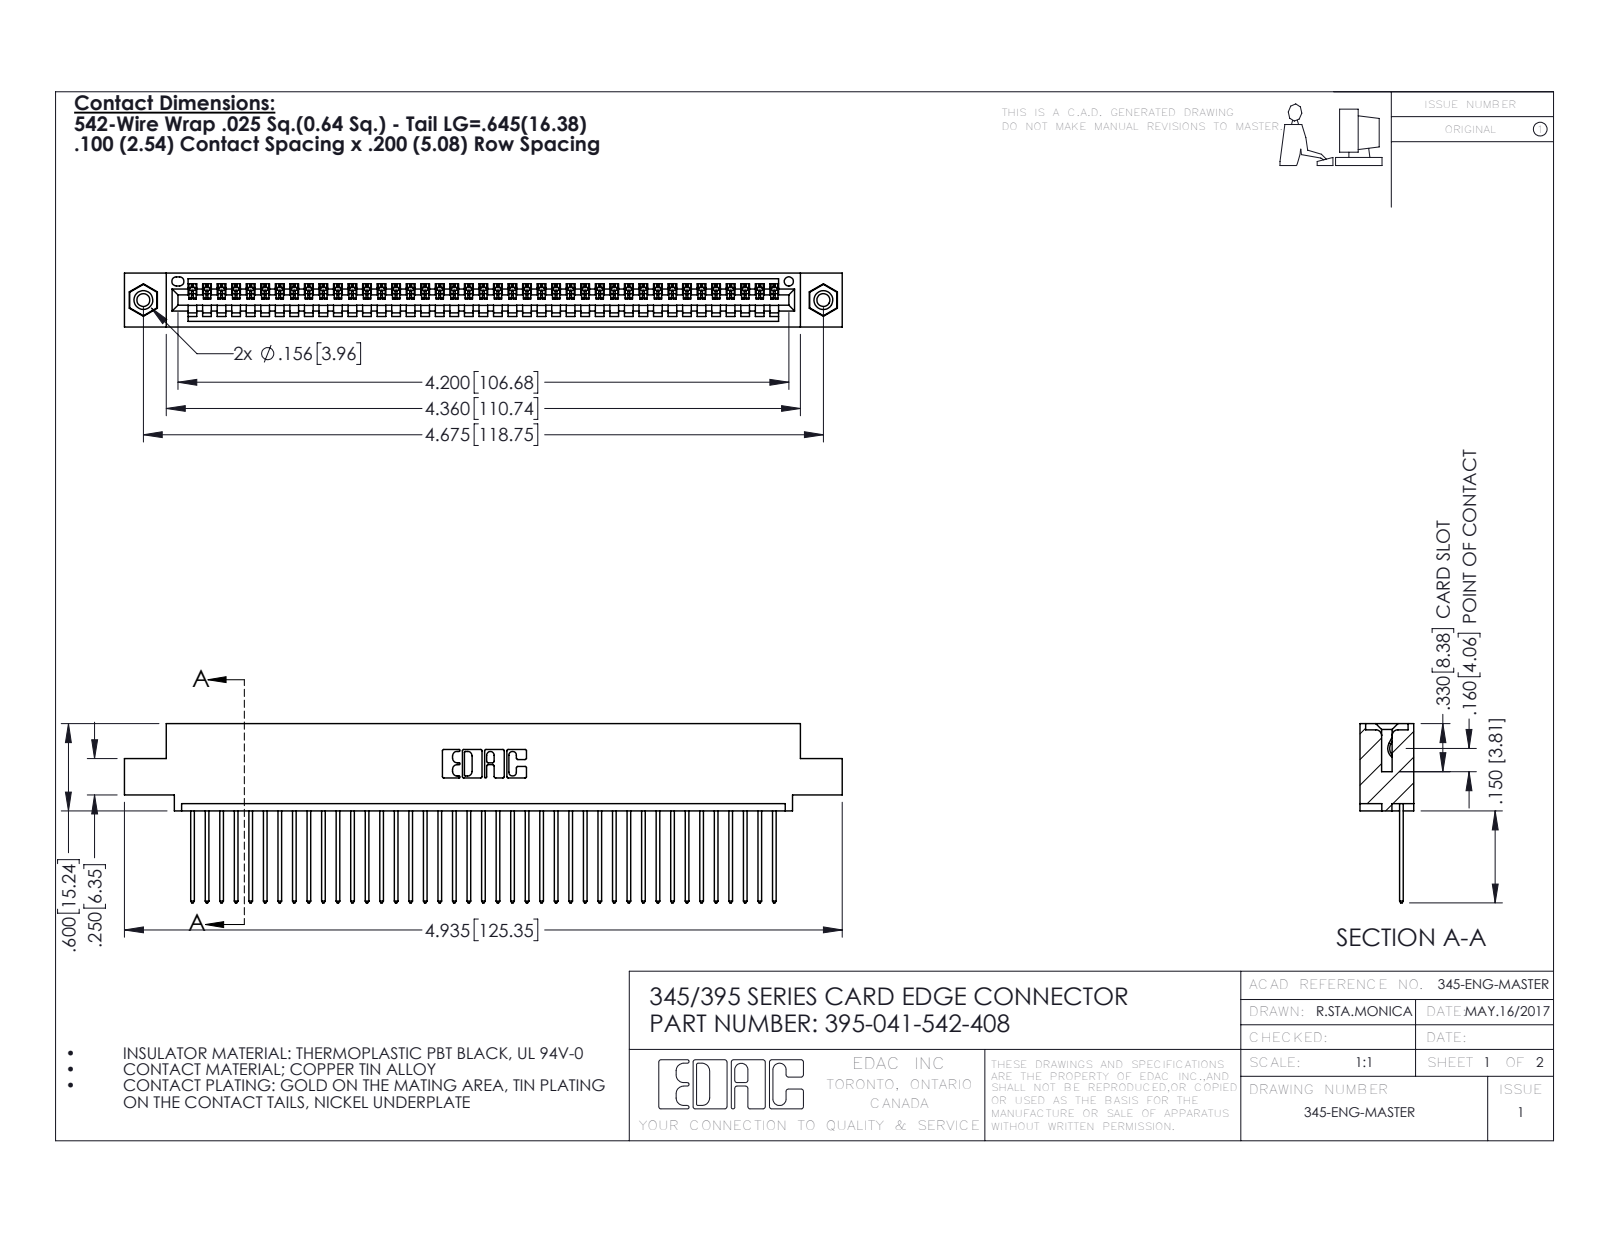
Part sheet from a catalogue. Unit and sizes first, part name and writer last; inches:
Units: inches
Overall size (bounding box): 4.935 × 1.232 × 0.37
Round holes (diameter × count): ⌀0.089 ×2, ⌀0.125 ×2, ⌀0.156 ×2, ⌀0.064 ×1
Round bosses / shafts (diameter × count): ⌀0.155 ×2
Partial cylindrical surfaces — rounded edges, fillets, slot ends (radius × count): R0.006 ×82, R0.01 ×82, R0.01 ×22, R0.007 ×6, R0.031 ×6, R0.026 ×3, R0.031 ×2, R0.04 ×2
Main face-to-face distances: 0.072, 0.298, 0.37, 0.098, 0.272, 0.025, 0.2, 0.225, 0.149, 0.072
Hole centre spacings: 0.27, 4.439, 4.675
Volume: 0.727 in³ · Surface area: 25.56 in²
Bodies: 44 solids, 2568 faces (1756 planar, 796 cylindrical, 16 other)
Part name (STEP PRODUCT): 345 Part_0.110 Offset - 0.156 Dia-TI; 395-041-542-408; 345-250-001_345-250-003-102; 345-292-001_345-293-142
STEP written by: SolidWorks 2016 (CONFIG_CONTROL_DESIGN)
